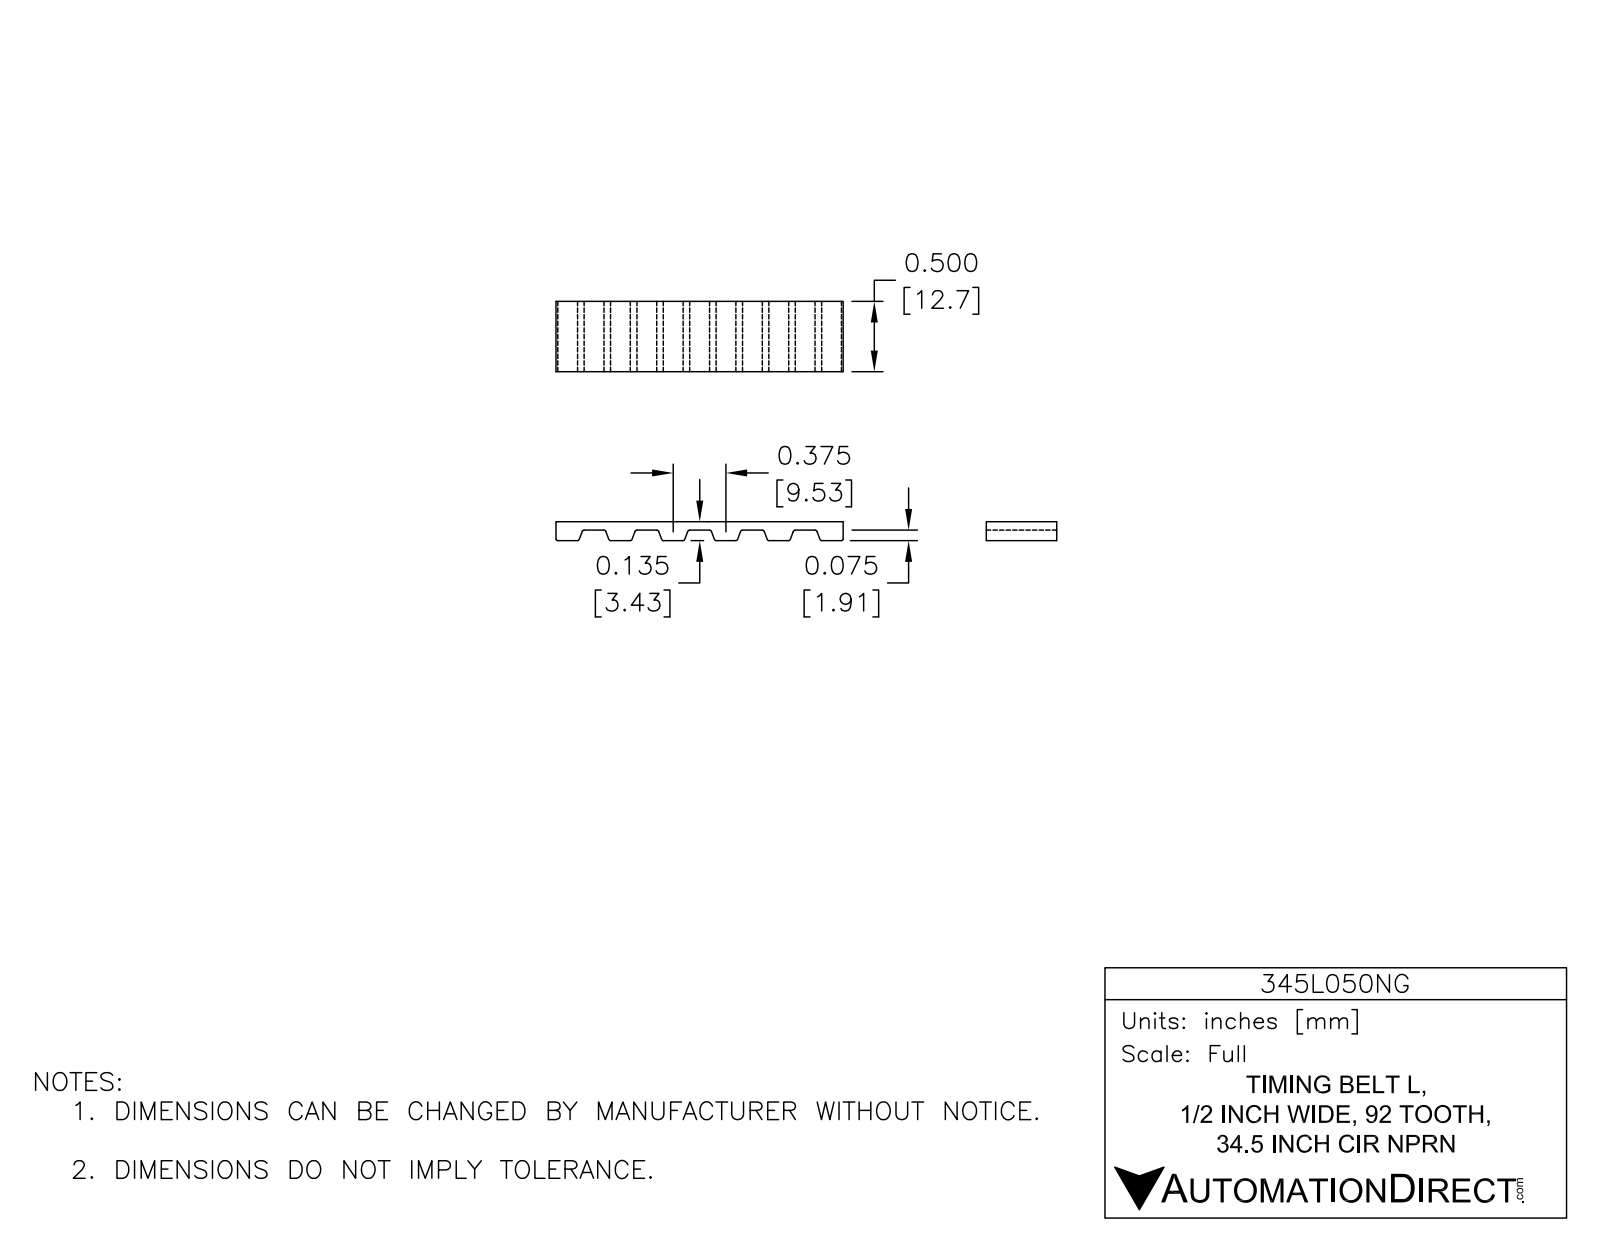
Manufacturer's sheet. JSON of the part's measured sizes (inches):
{"part_name": "345L050NG", "step_written_by": "SolidWorks 2014 (AUTOMOTIVE_DESIGN)", "units": "inches", "bodies": {"solids": 1, "faces": 751, "planar": 345, "cylindrical": 406, "other": 0}, "overall_size": [15.538, 3, 0.5], "volume_in3": 1.562, "surface_area_in2": 44.66, "partial_cylinders_radius": [[0.02, 364], [1.435, 2], [1.5, 2]], "face_to_face_distances": [0.065, 2.935, 3, 2.87, 0.5, 0.14, 2.86, 0.075, 2.795, 2.72]}
